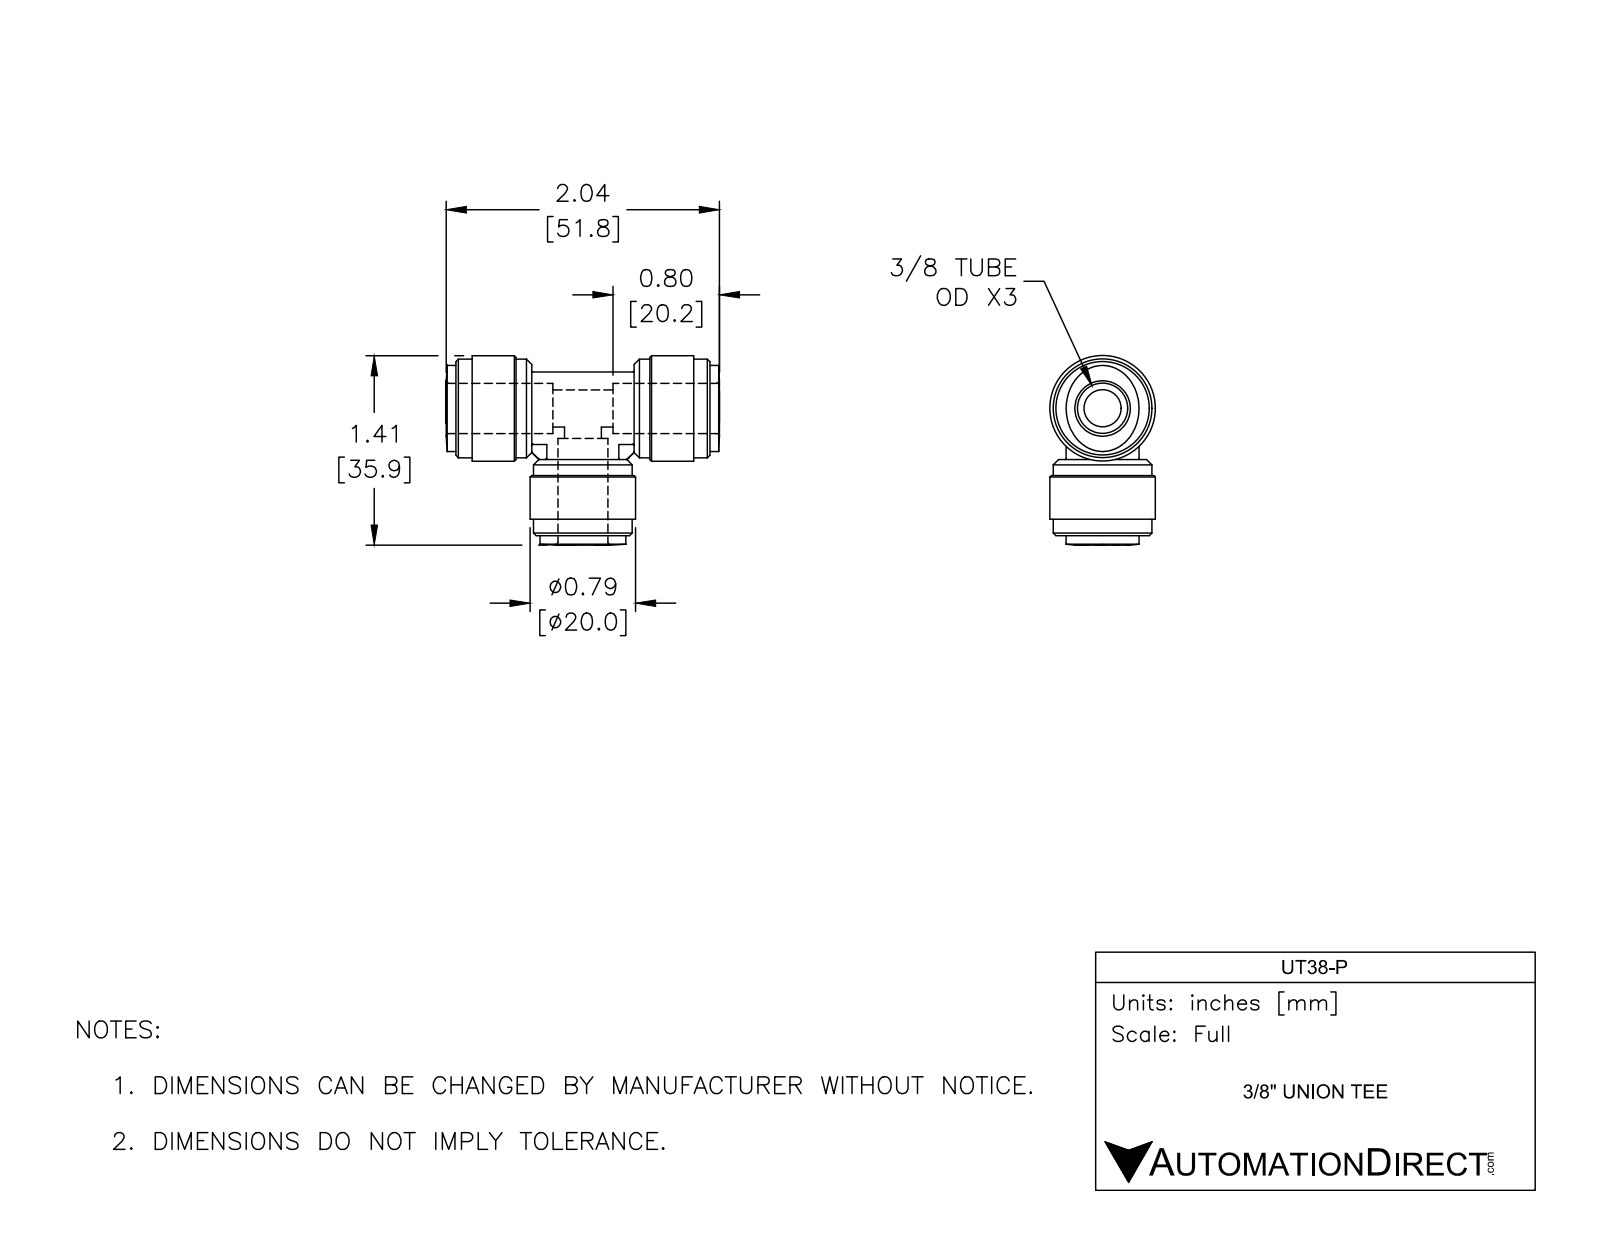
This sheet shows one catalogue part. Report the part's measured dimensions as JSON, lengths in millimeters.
{"part_name": "UT38-P", "step_written_by": "SolidWorks 2017 (AUTOMOTIVE_DESIGN)", "units": "millimeters", "bodies": {"solids": 1, "faces": 98, "planar": 20, "cylindrical": 33, "other": 45}, "overall_size": [51.8, 35.9, 20], "volume_mm3": 12300, "surface_area_mm2": 6942, "round_holes": [[7, 2], [9.5, 2]], "round_bosses_or_shafts": [[20, 2], [18.7, 2], [13.8, 2]], "face_to_face_distances": [14.4, 18.4, 3.1, 11.3, 33.8, 15.3, 4, 11.4, 45.1, 30.7]}
